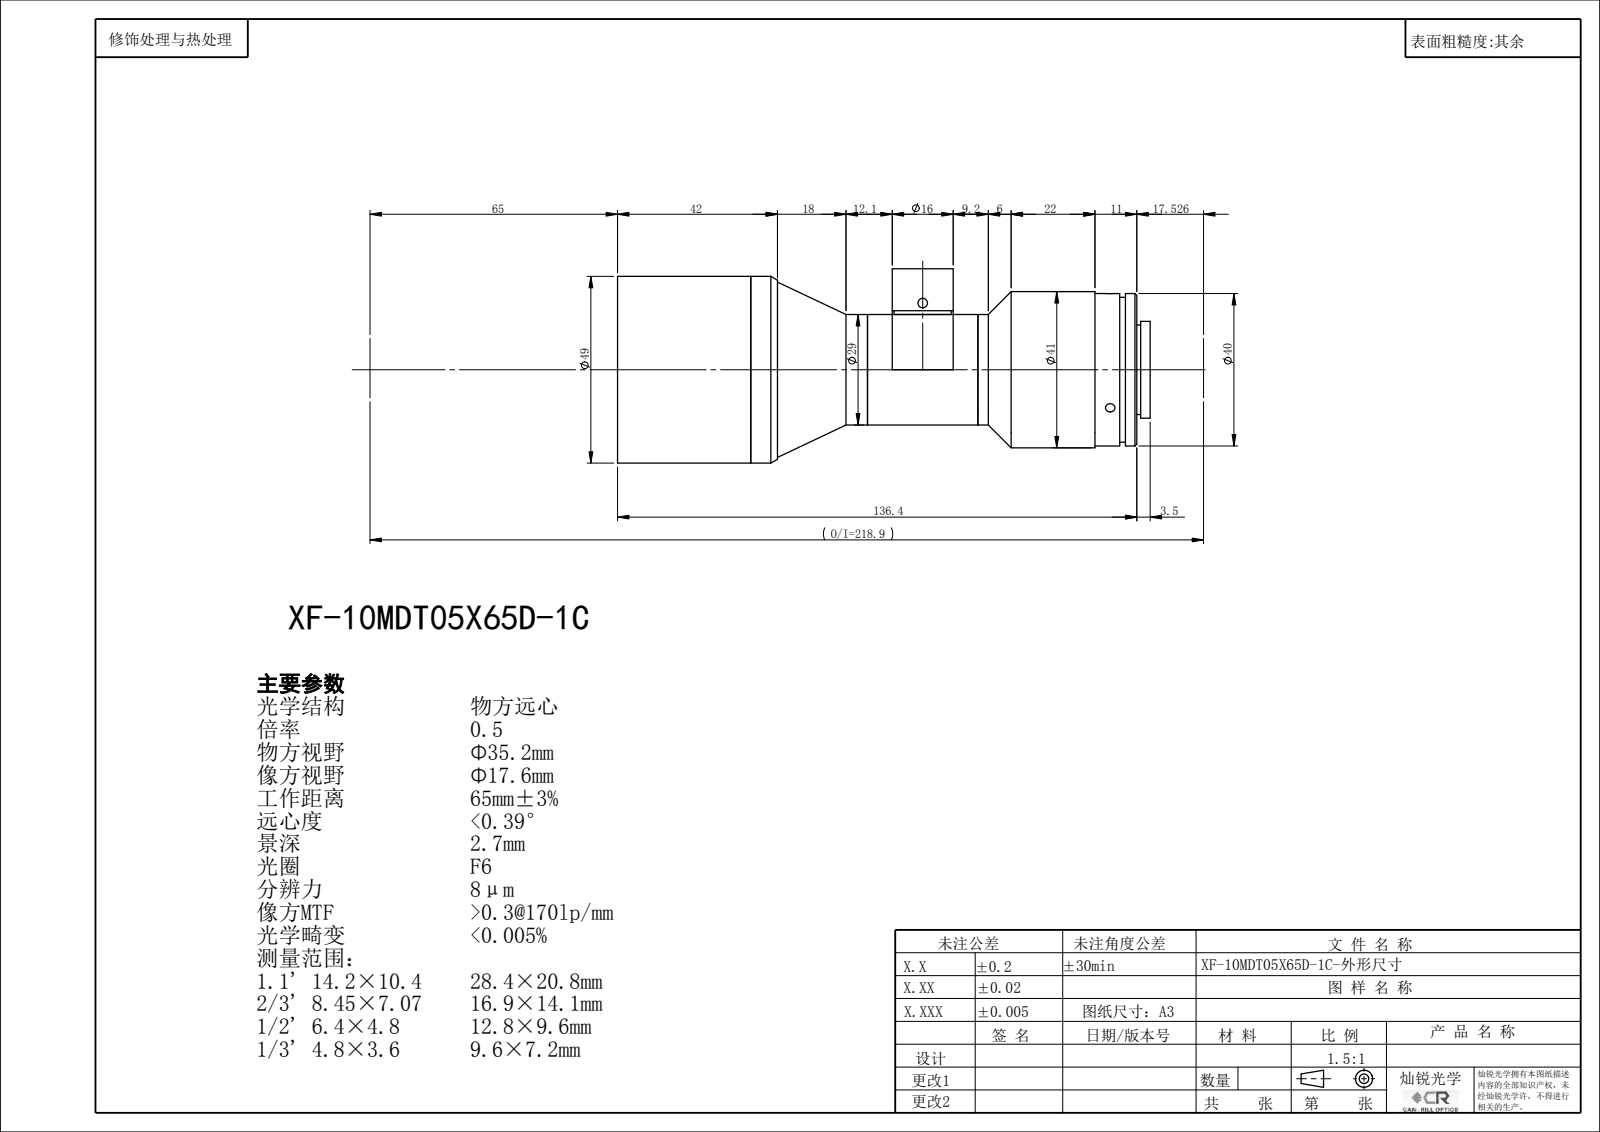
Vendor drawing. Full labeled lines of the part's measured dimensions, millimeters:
STEP written by: SolidWorks 2014 (CONFIG_CONTROL_DESIGN)
Units: millimetres
Bodies: 0 solids, 112 faces (39 planar, 61 cylindrical, 12 other)
Overall size (bounding box): 139.87 × 51 × 49
Round holes (diameter × count): ⌀2.2 ×4, ⌀2.5 ×4, ⌀1.6 ×2, ⌀8 ×1, ⌀14 ×1, ⌀19 ×1, ⌀21.4 ×1, ⌀43 ×1, ⌀45.4 ×1, ⌀46 ×1
Round bosses / shafts (diameter × count): ⌀49 ×1, ⌀41 ×1, ⌀40 ×1, ⌀38 ×1, ⌀29 ×1, ⌀25.4 ×1, ⌀23.5 ×1, ⌀16 ×1
Main face-to-face distances: 11, 90.37, 101.37, 99.37, 9, 2, 6.5, 1, 29, 35
Hole centre spacings: 11.66, 12, 20, 23.32, 44.37, 56.13, 49.23
